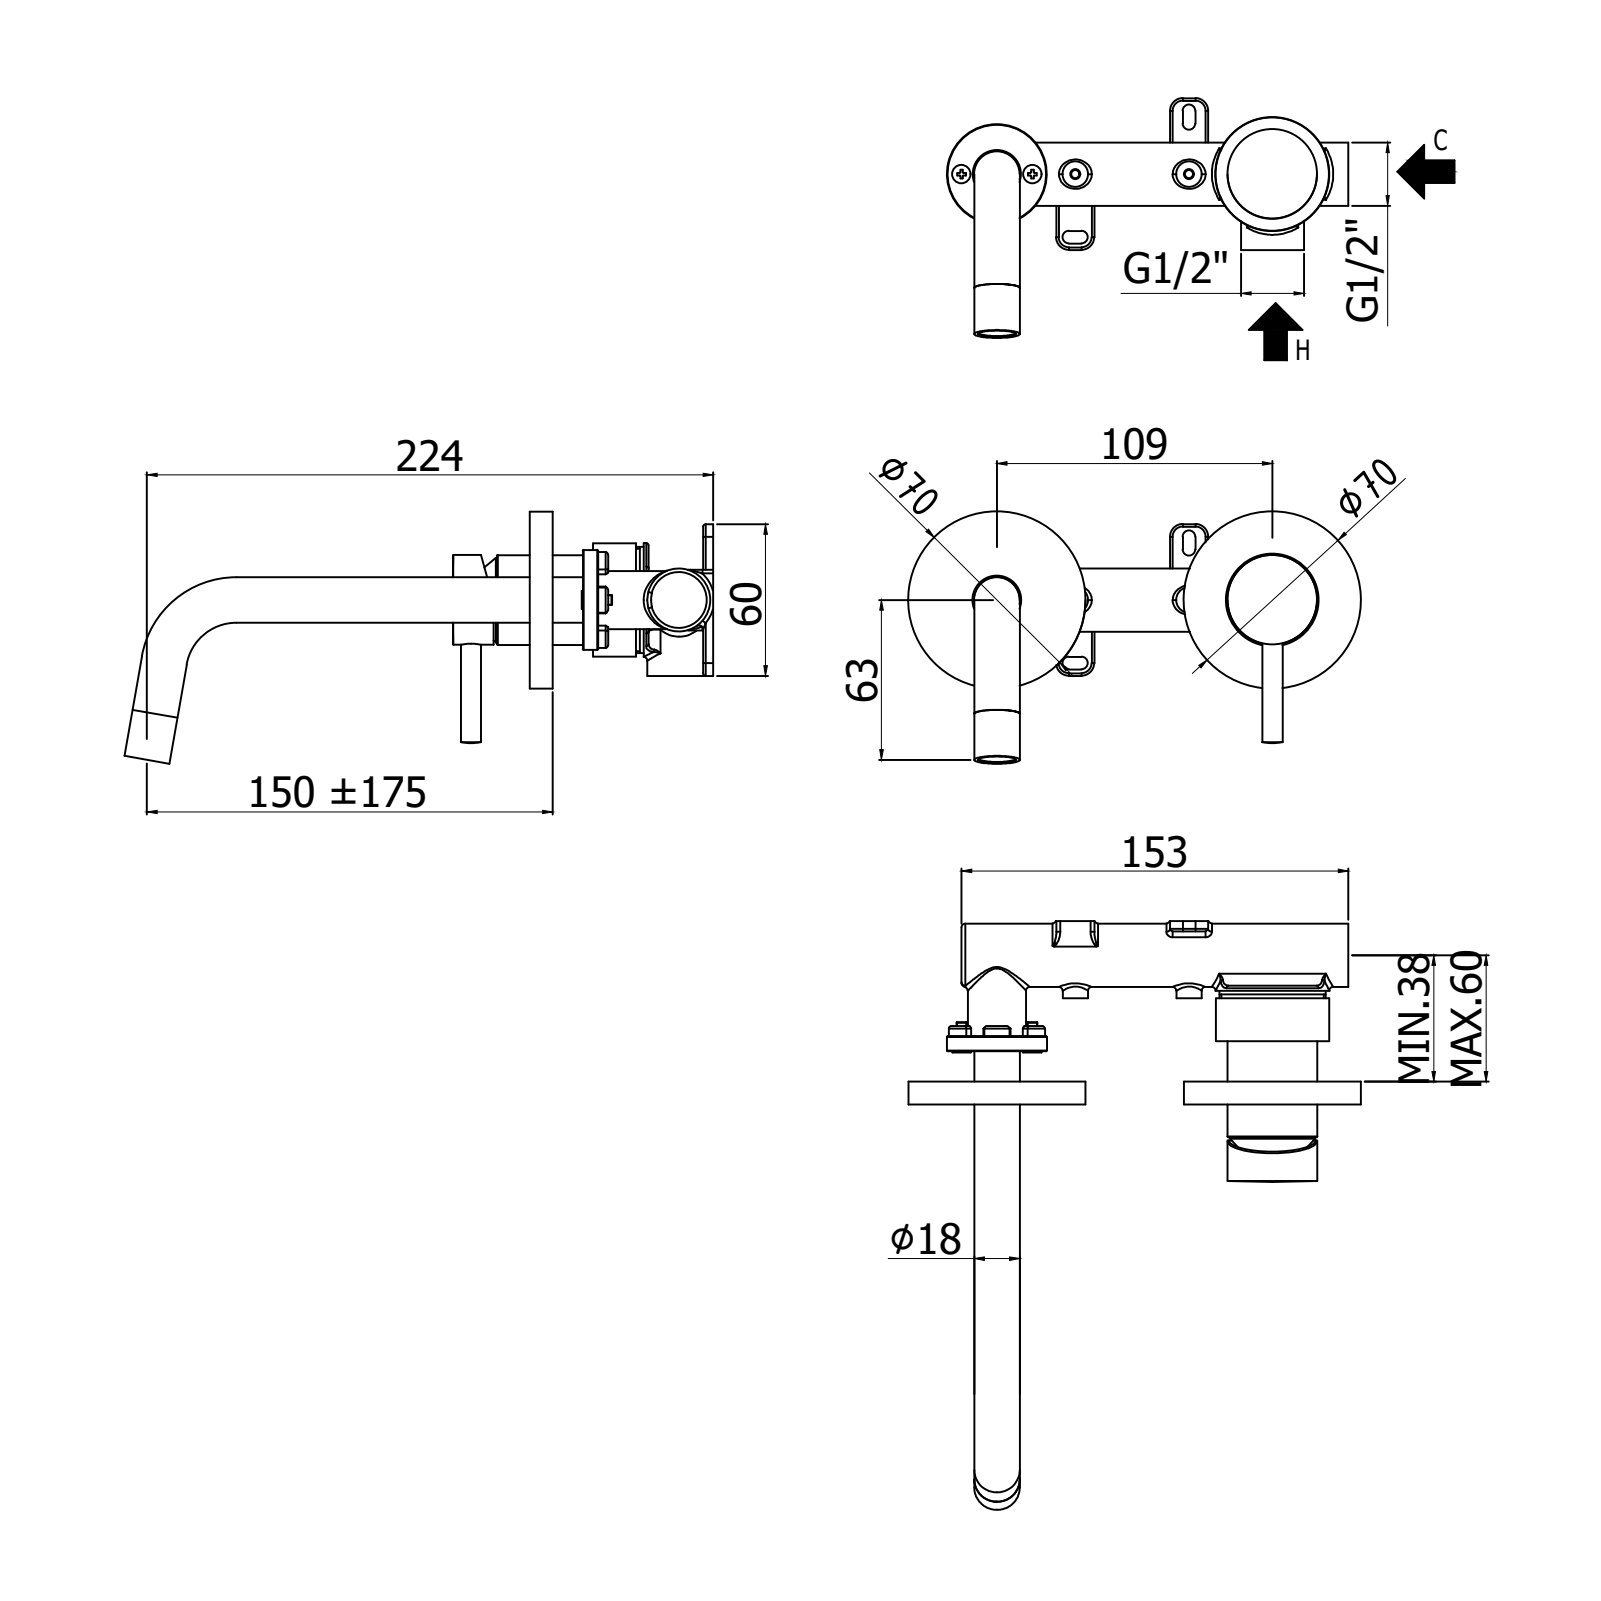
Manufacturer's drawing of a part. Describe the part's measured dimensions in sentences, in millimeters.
The part is named "SK101CR70". Its 3-D file was written by "CREO PARAMETRIC BY PTC INC, 2020044 (CONFIG_CONTROL_DESIGN)". It is 3 solids with 123 faces: 48 planar, 45 cylindrical and 30 other. Overall it measures 179 by 174.38 by 99.78 millimeters. Its volume is 140 080 cubic millimeters and its surface area 44 820 square millimeters. Round holes: 1 of diameter 5.6, 1 of diameter 18, 1 of diameter 22.5, 1 of diameter 25.5, 1 of diameter 30, 1 of diameter 31.5. Round bosses or shafts: 2 of diameter 70, 2 of diameter 35.5, 2 of diameter 18, 1 of diameter 33.5, 1 of diameter 28, 1 of diameter 8. Partial cylindrical surfaces (rounded edges, fillets, slot ends): 2 of radius 2.5, 1 of radius 8.3, 1 of radius 12. The main face-to-face distances are 9, 37.8, 28.8, 14.5, 11.5, 32.41, 23.41, 5.39, 3.5, 32.5.
